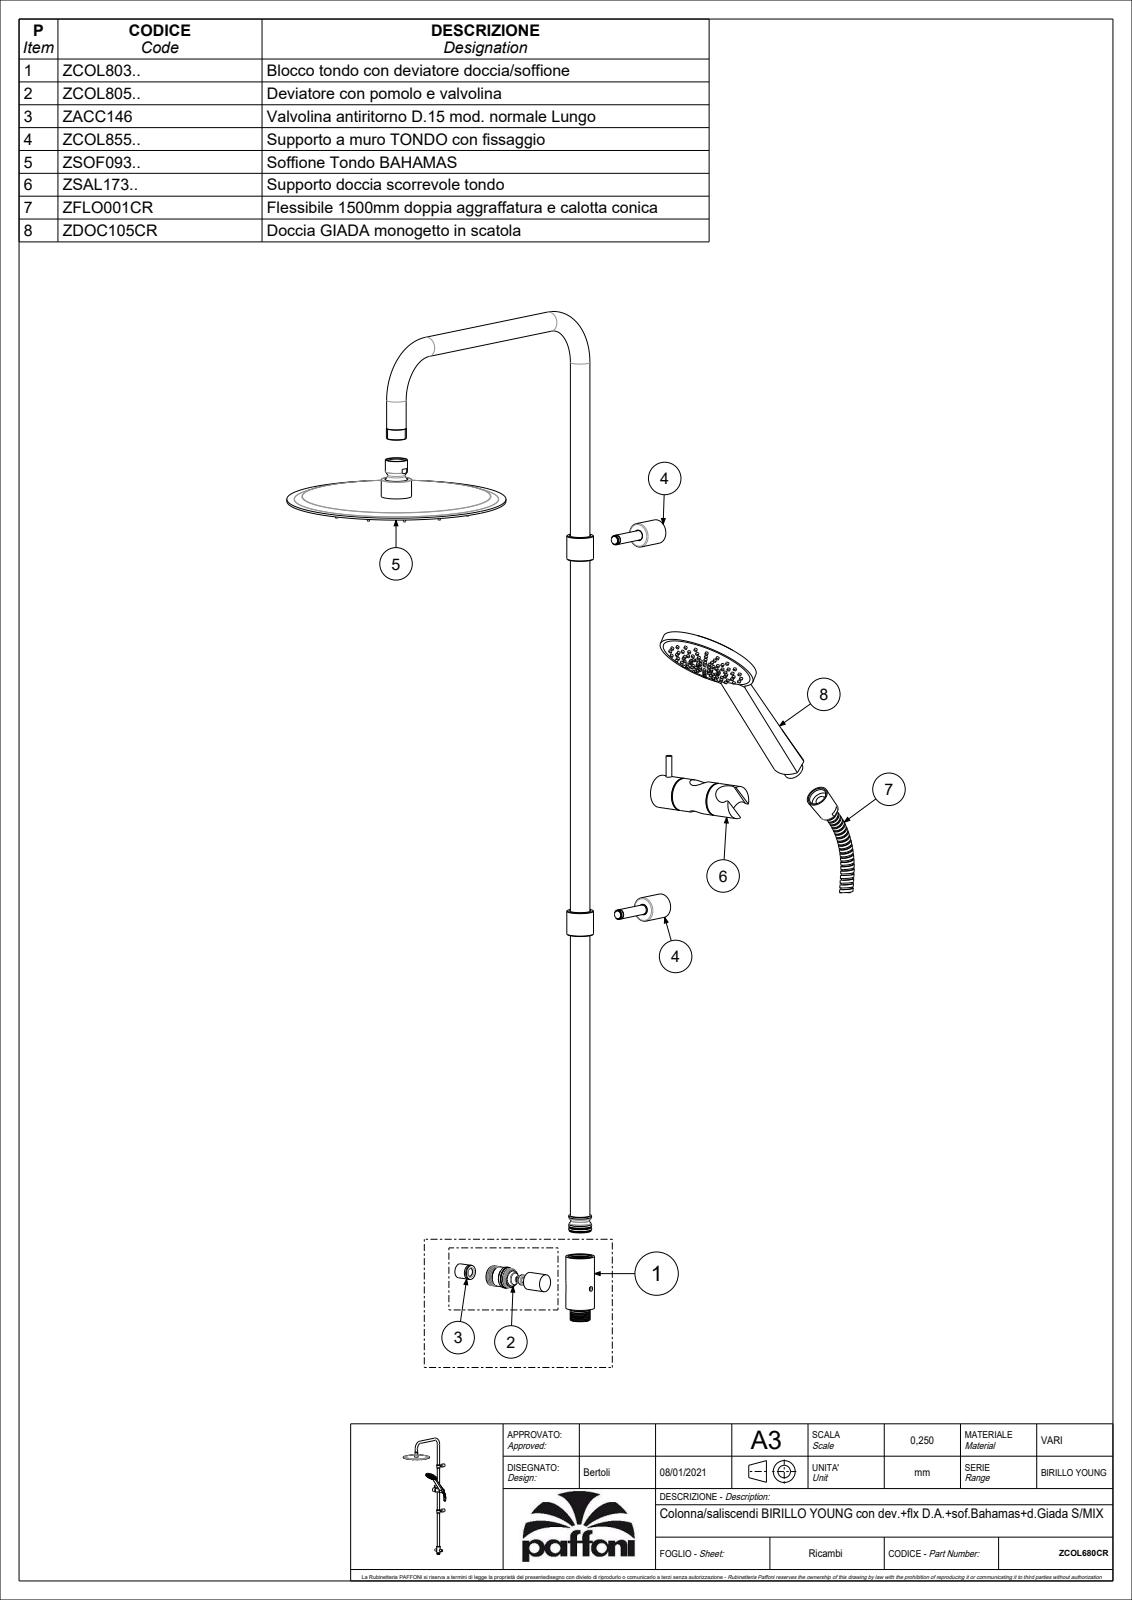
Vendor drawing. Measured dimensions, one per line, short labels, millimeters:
name: ZCOL680CR
written by: CREO PARAMETRIC BY PTC INC, 2020044 (CONFIG_CONTROL_DESIGN)
unit: mm
bodies: 6 solids, 3291 faces (487 planar, 901 cylindrical, 1903 other)
size: 1037.75 × 490 × 230
volume: 652 785 mm³; area: 428 388 mm²
holes: 76× ⌀1.5, 76× ⌀1.7, 4× ⌀5, 3× ⌀17, 2× ⌀4.2, 2× ⌀6.5, 2× ⌀9, 2× ⌀10.2, 2× ⌀10.5, 2× ⌀15, 2× ⌀16.5, 2× ⌀24
bosses: 90× ⌀3, 78× ⌀10, 4× ⌀20.5, 2× ⌀28, 2× ⌀25, 2× ⌀21, 2× ⌀8.5, 2× ⌀5
rounds: 1× R5.4, 1× R6.1, 1× R9.91, 1× R12
face distances: 1, 4, 3, 5, 2, 2.4, 1.4, 1.6, 2.6, 0.4
hole spacings: 38.65, 97.5, 126.12, 38.04, 162.14, 191.25, 69.82, 99.68
